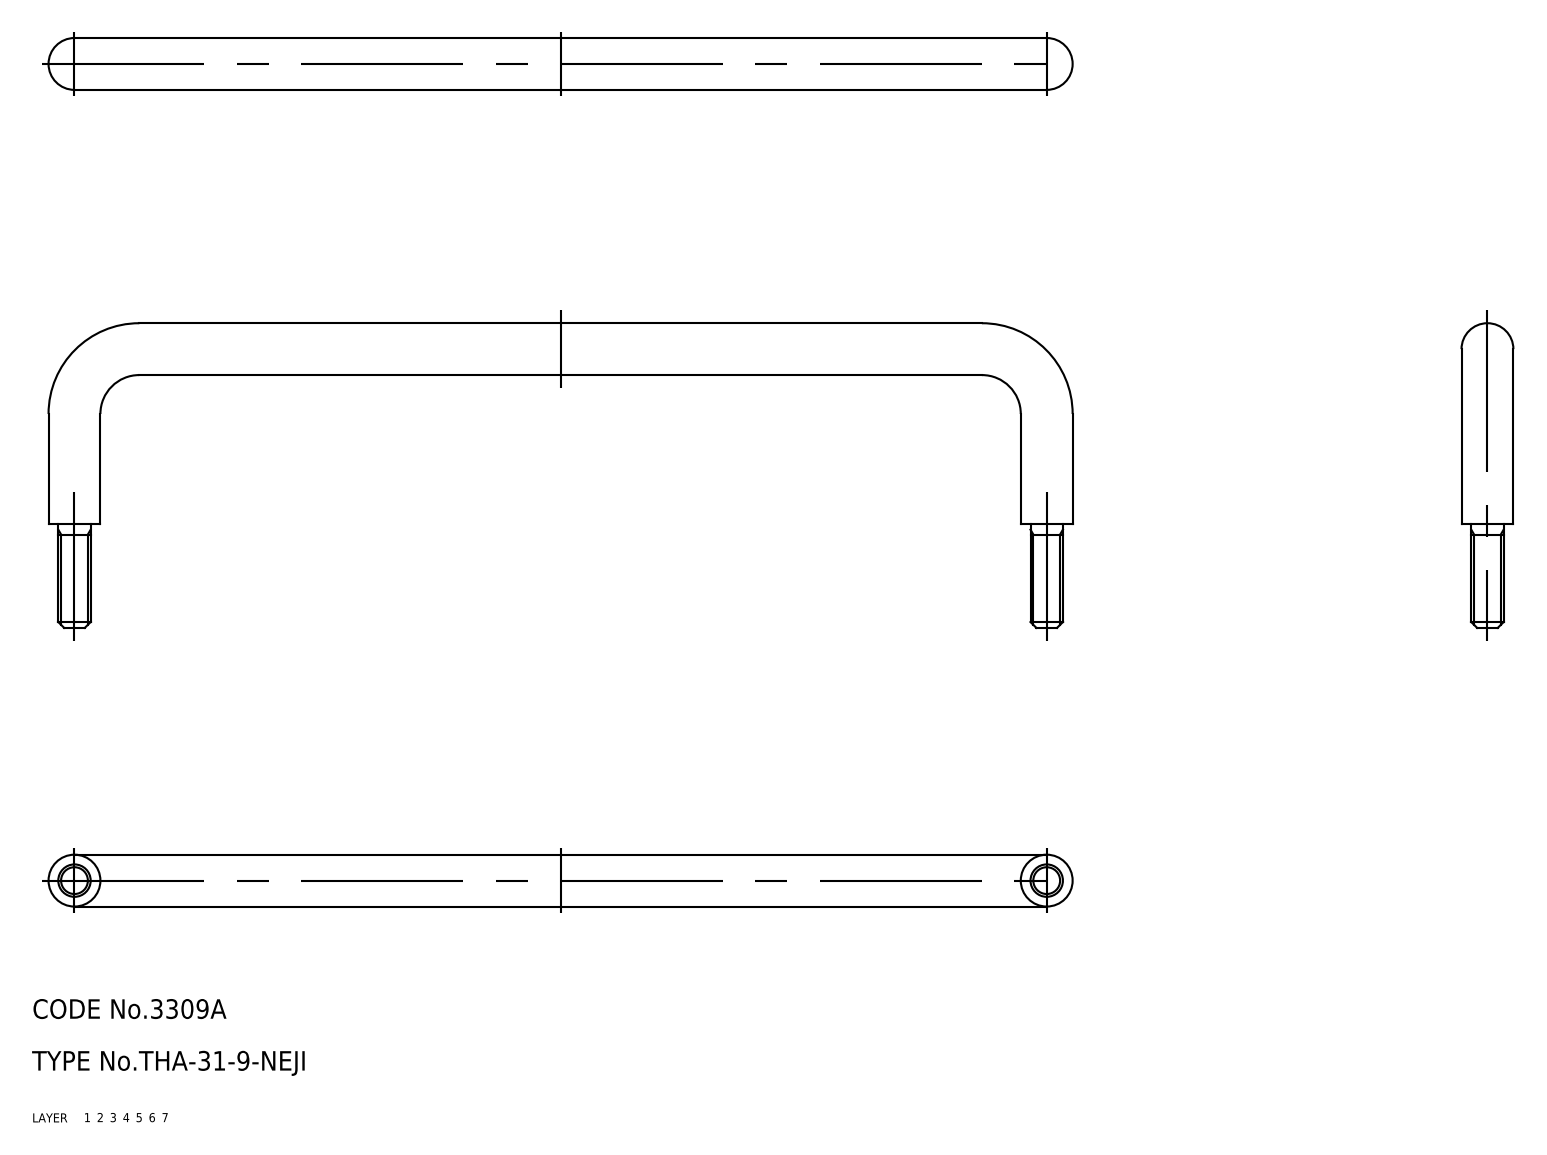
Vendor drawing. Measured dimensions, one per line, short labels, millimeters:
name: pull
written by: CADfix (AUTOMOTIVE_DESIGN)
unit: mm
bodies: 1 solid, 22 faces (0 planar, 0 cylindrical, 22 other)
size: 158 × 47 × 8
volume: 10 479 mm³; area: 5 499 mm²
